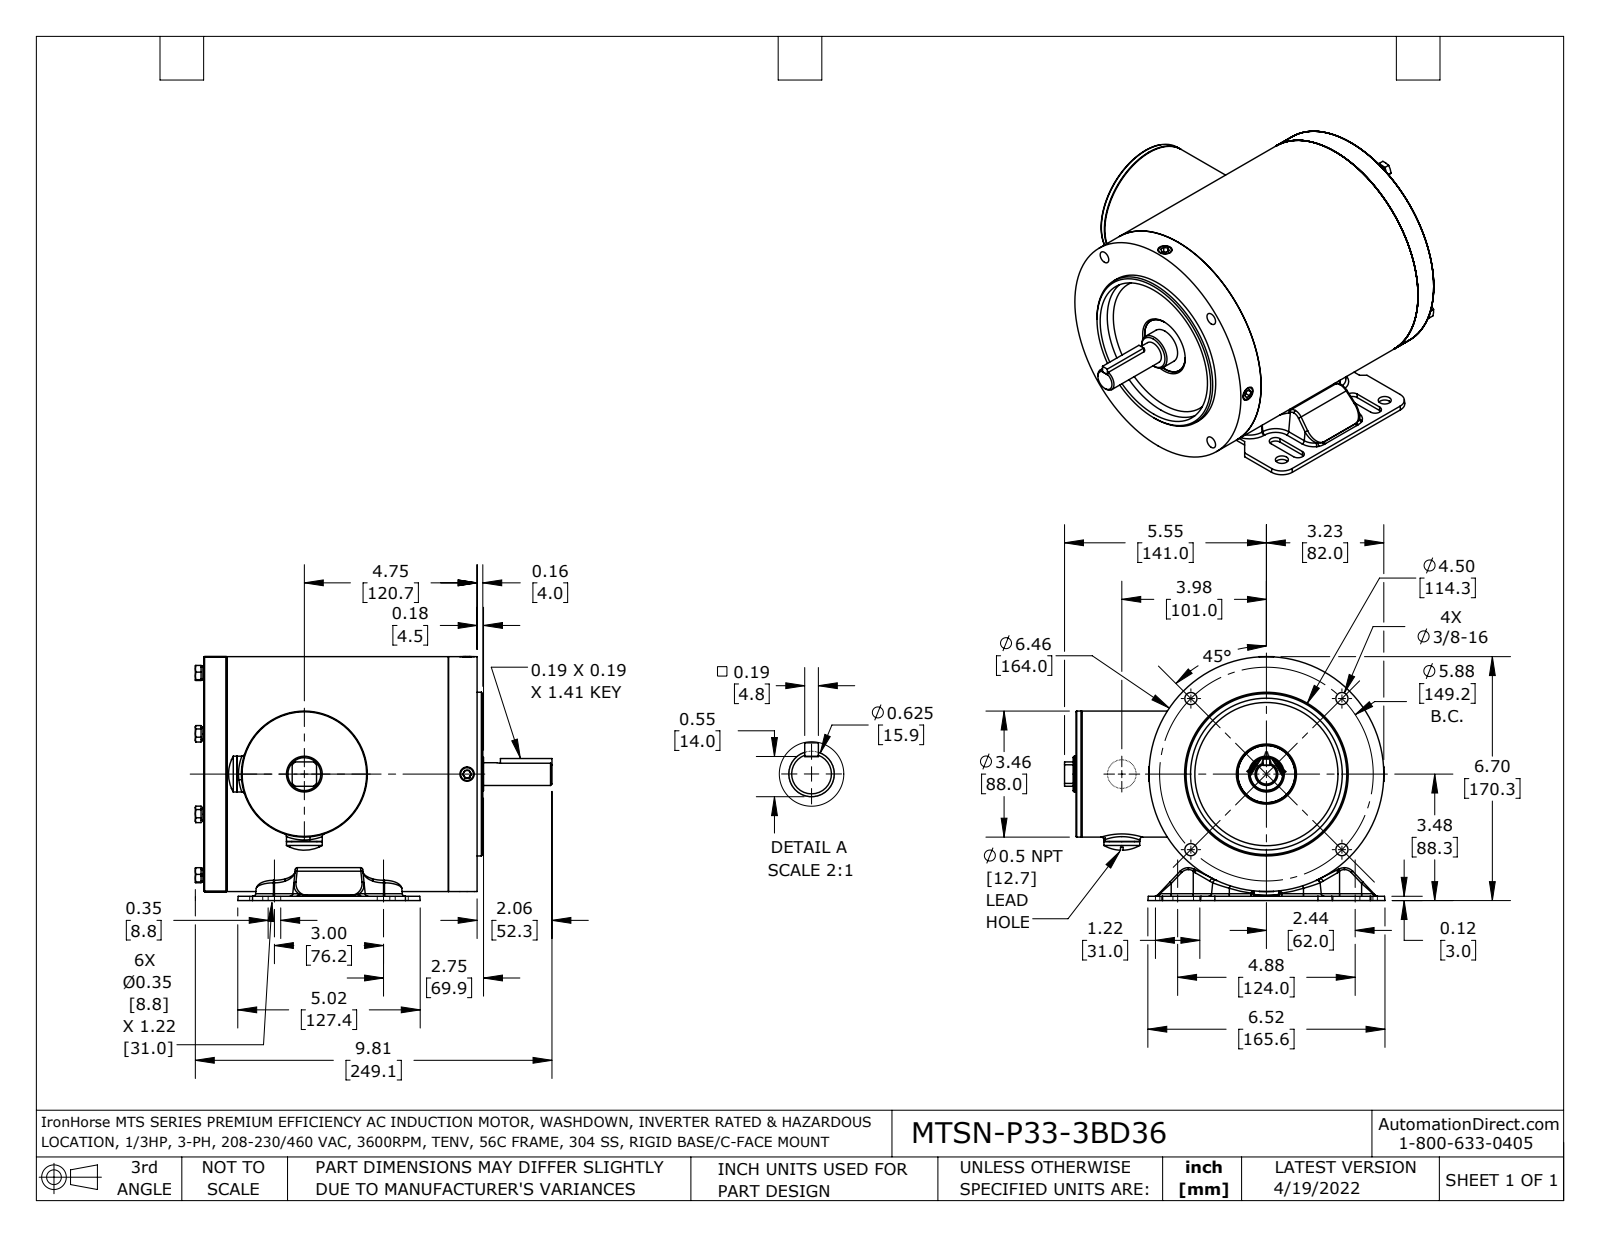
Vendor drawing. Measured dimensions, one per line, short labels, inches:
name: H(MTSN-P33-3BD18) nc WITH-bolts redcmb1 coord fxt
written by: SolidWorks 2021 (AUTOMOTIVE_DESIGN)
unit: in
bodies: 8 solids, 909 faces (277 planar, 312 cylindrical, 320 other)
size: 9.807 × 8.812 × 6.705
volume: 46.66 in³; area: 669.6 in²
holes: 6× ⌀0.165, 4× ⌀0.256, 4× ⌀0.335, 4× ⌀0.358, 2× ⌀0.118, 2× ⌀0.656, 2× ⌀1.378, 1× ⌀1.024, 1× ⌀1.654, 1× ⌀2.047, 1× ⌀2.598, 1× ⌀3.071
bosses: 6× ⌀0.394, 4× ⌀0.984, 4× ⌀0.315, 4× ⌀0.236, 2× ⌀0.787, 2× ⌀0.692, 1× ⌀4.5, 1× ⌀4.409
rounds: 42× R0.079, 8× R0.173, 6× R0.059, 6× R0.315, 5× R0.118, 4× R0.039, 4× R0.197, 4× R0.217
face distances: 0.118, 7.382, 0.236, 7.264, 7.146, 7.5, 0.354, 7.028, 0.157, 0.433
hole spacings: 2.937, 4.154, 1.181, 1.917, 2.231, 2.498, 3.234, 3.459
